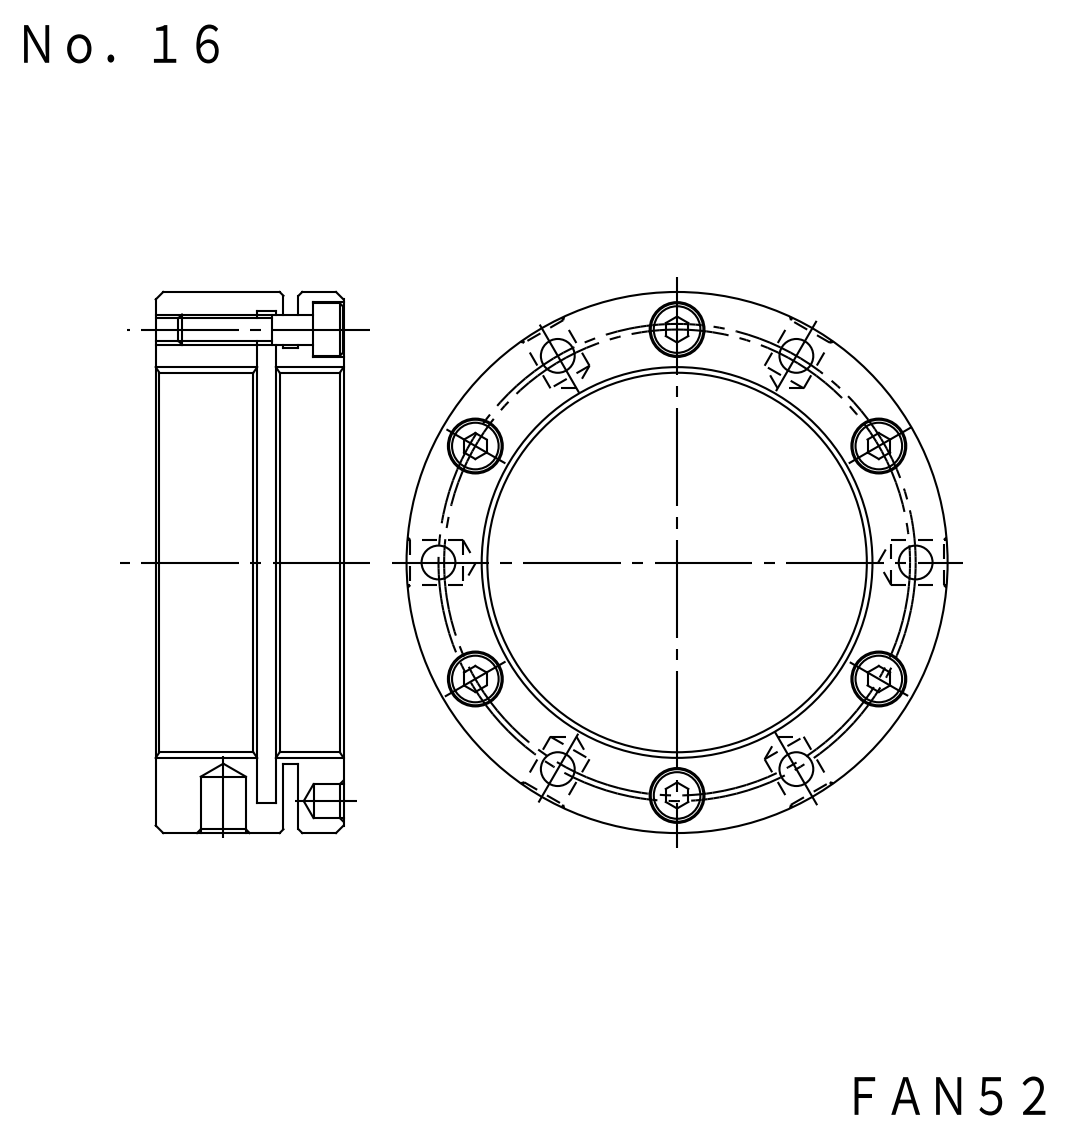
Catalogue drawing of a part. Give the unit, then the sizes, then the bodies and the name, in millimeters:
Units: millimetres
Overall size (bounding box): 72 × 72 × 25
Round holes (diameter × count): ⌀3.24 ×6, ⌀4.3 ×6, ⌀4.5 ×6, ⌀7.3 ×6, ⌀6 ×3, ⌀52 ×1, ⌀67 ×1
Round bosses / shafts (diameter × count): ⌀7 ×6, ⌀4 ×6, ⌀72 ×1, ⌀57 ×1
Main face-to-face distances: 6, 25, 4, 2, 17, 8, 19, 13, 12, 15.5
Hole centre spacings: 31, 16.26, 60.62, 31.75, 44.38, 53.7, 31.76, 44.37
Volume: 40 669 mm³ · Surface area: 24 291 mm²
Bodies: 7 solids, 204 faces (72 planar, 108 cylindrical, 24 other)
Part name (STEP PRODUCT): FKD FAN52; M4X18_default
STEP written by: SolidWorks 2012 (CONFIG_CONTROL_DESIGN)
